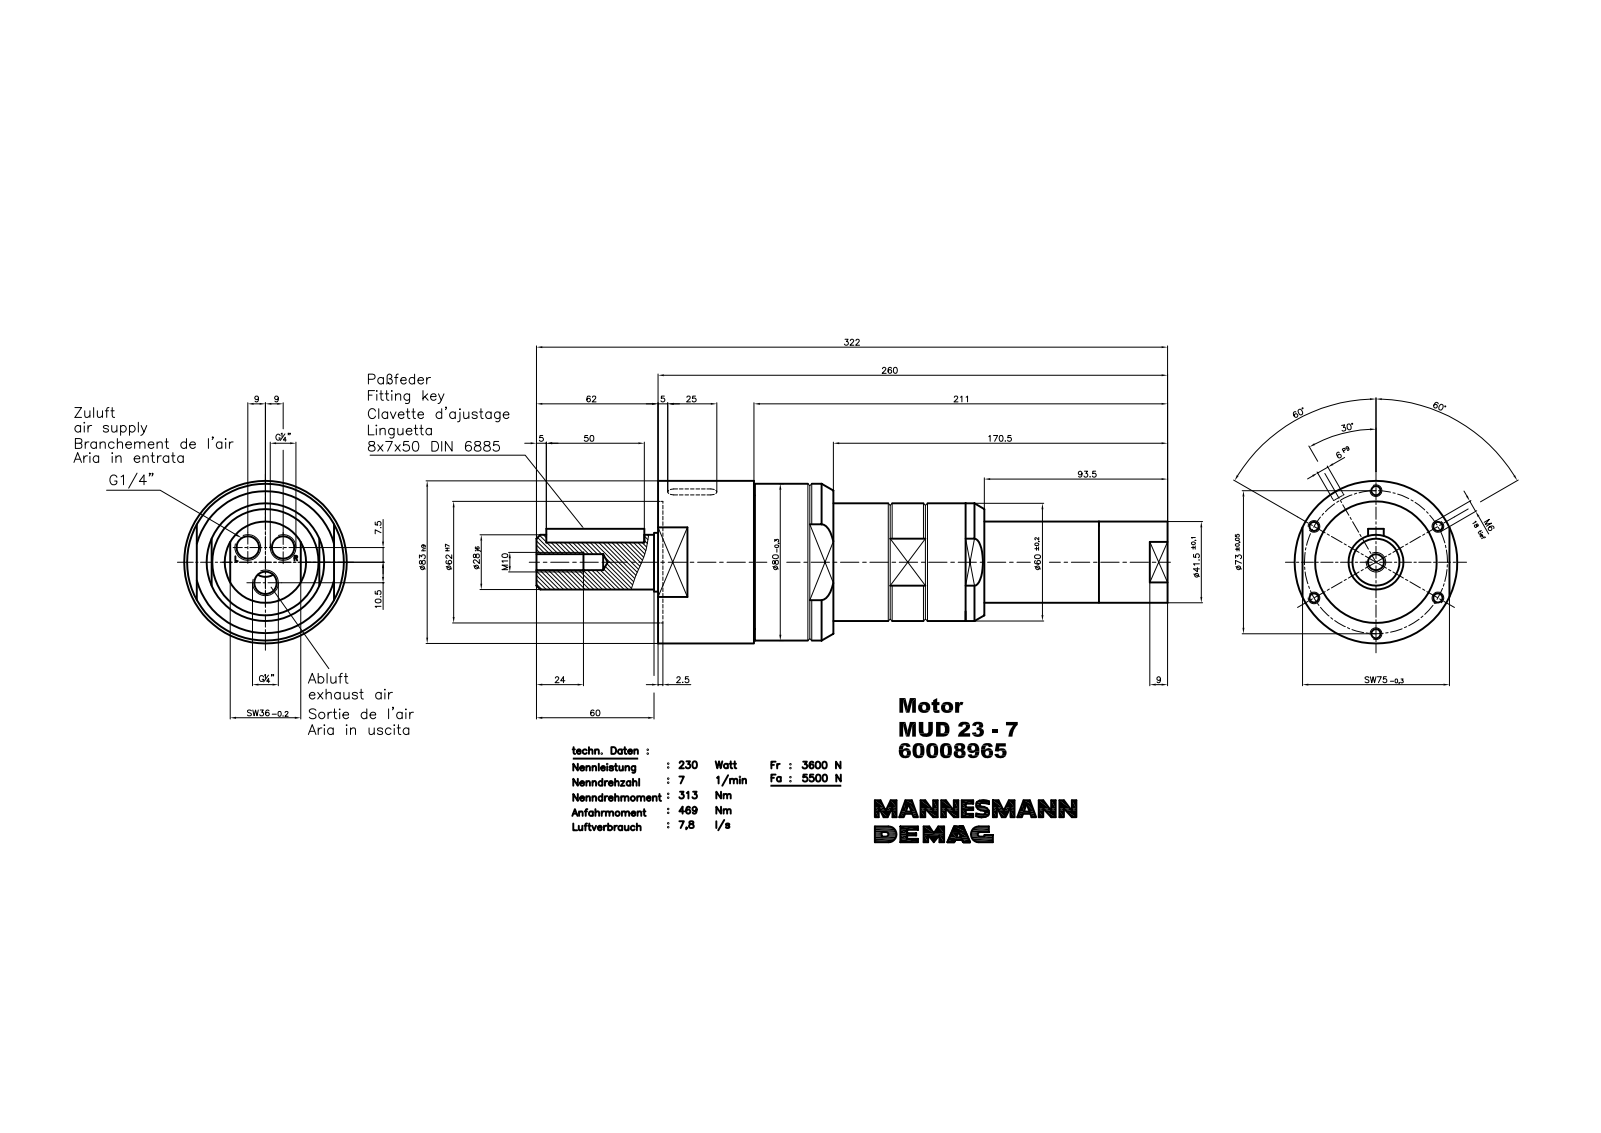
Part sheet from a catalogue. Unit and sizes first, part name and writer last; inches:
Units: inches
Overall size (bounding box): 12.677 × 3.268 × 3.268
Round holes (diameter × count): ⌀0.061 ×2, ⌀0.157 ×2, ⌀0.217 ×2, ⌀1.496 ×1, ⌀1.654 ×1, ⌀2.311 ×1, ⌀2.441 ×1
Round bosses / shafts (diameter × count): ⌀0.197 ×2, ⌀0.142 ×2, ⌀3.268 ×1, ⌀3.15 ×1, ⌀2.891 ×1, ⌀2.362 ×1, ⌀1.772 ×1, ⌀1.634 ×1
Partial cylindrical surfaces — rounded edges, fillets, slot ends (radius × count): R0.089 ×2, R0.118 ×2, R0.157 ×2, R1.28 ×2, R1.062 ×1
Main face-to-face distances: 0.142, 3.524, 3.381, 0.02, 1.929, 1.787, 1.594, 3.031, 10.236, 10.094
Volume: 50.1 in³ · Surface area: 116.2 in²
Bodies: 1 solid, 225 faces (121 planar, 45 cylindrical, 59 other)
Part name (STEP PRODUCT): MUD 23-7_60008965
STEP written by: Autodesk Inventor 2008 (CONFIG_CONTROL_DESIGN)
